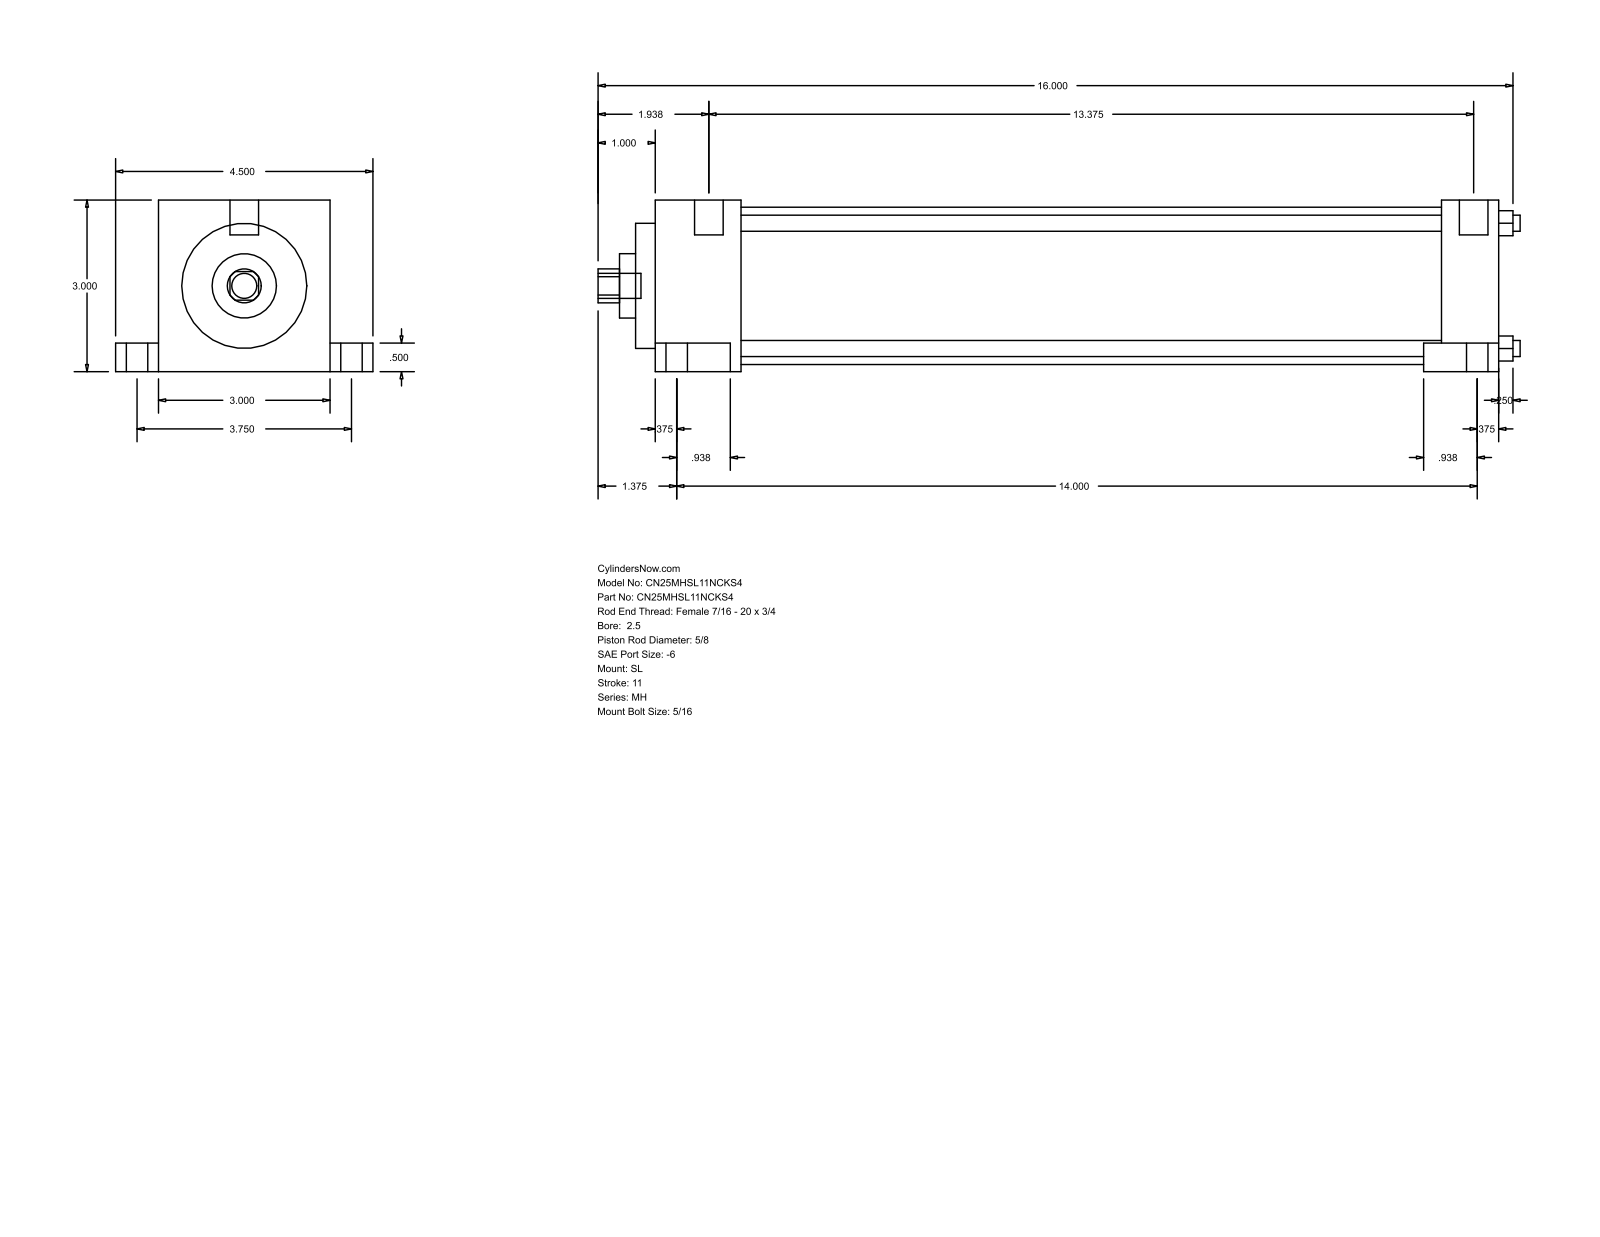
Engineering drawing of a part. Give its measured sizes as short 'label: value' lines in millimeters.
name: MH_SL__0250_0.625
written by: GSSL Pune (CONFIG_CONTROL_DESIGN)
unit: mm
bodies: 0 solids, 86 faces (61 planar, 25 cylindrical, 0 other)
size: 409.57 × 114.3 × 76.2
holes: 4× ⌀7.14, 1× ⌀15.88, 1× ⌀28.57, 1× ⌀55.55, 1× ⌀69.85
bosses: 2× ⌀15.88, 2× ⌀9.53, 2× ⌀5.56, 1× ⌀12.7, 1× ⌀11.11
rounds: 1× R7.54
face distances: 76.2, 25.4, 357.98, 383.38, 12.7, 63.5, 19.05, 95.25, 390.52, 31.75
hole spacings: 39.33, 55.62, 78.66
